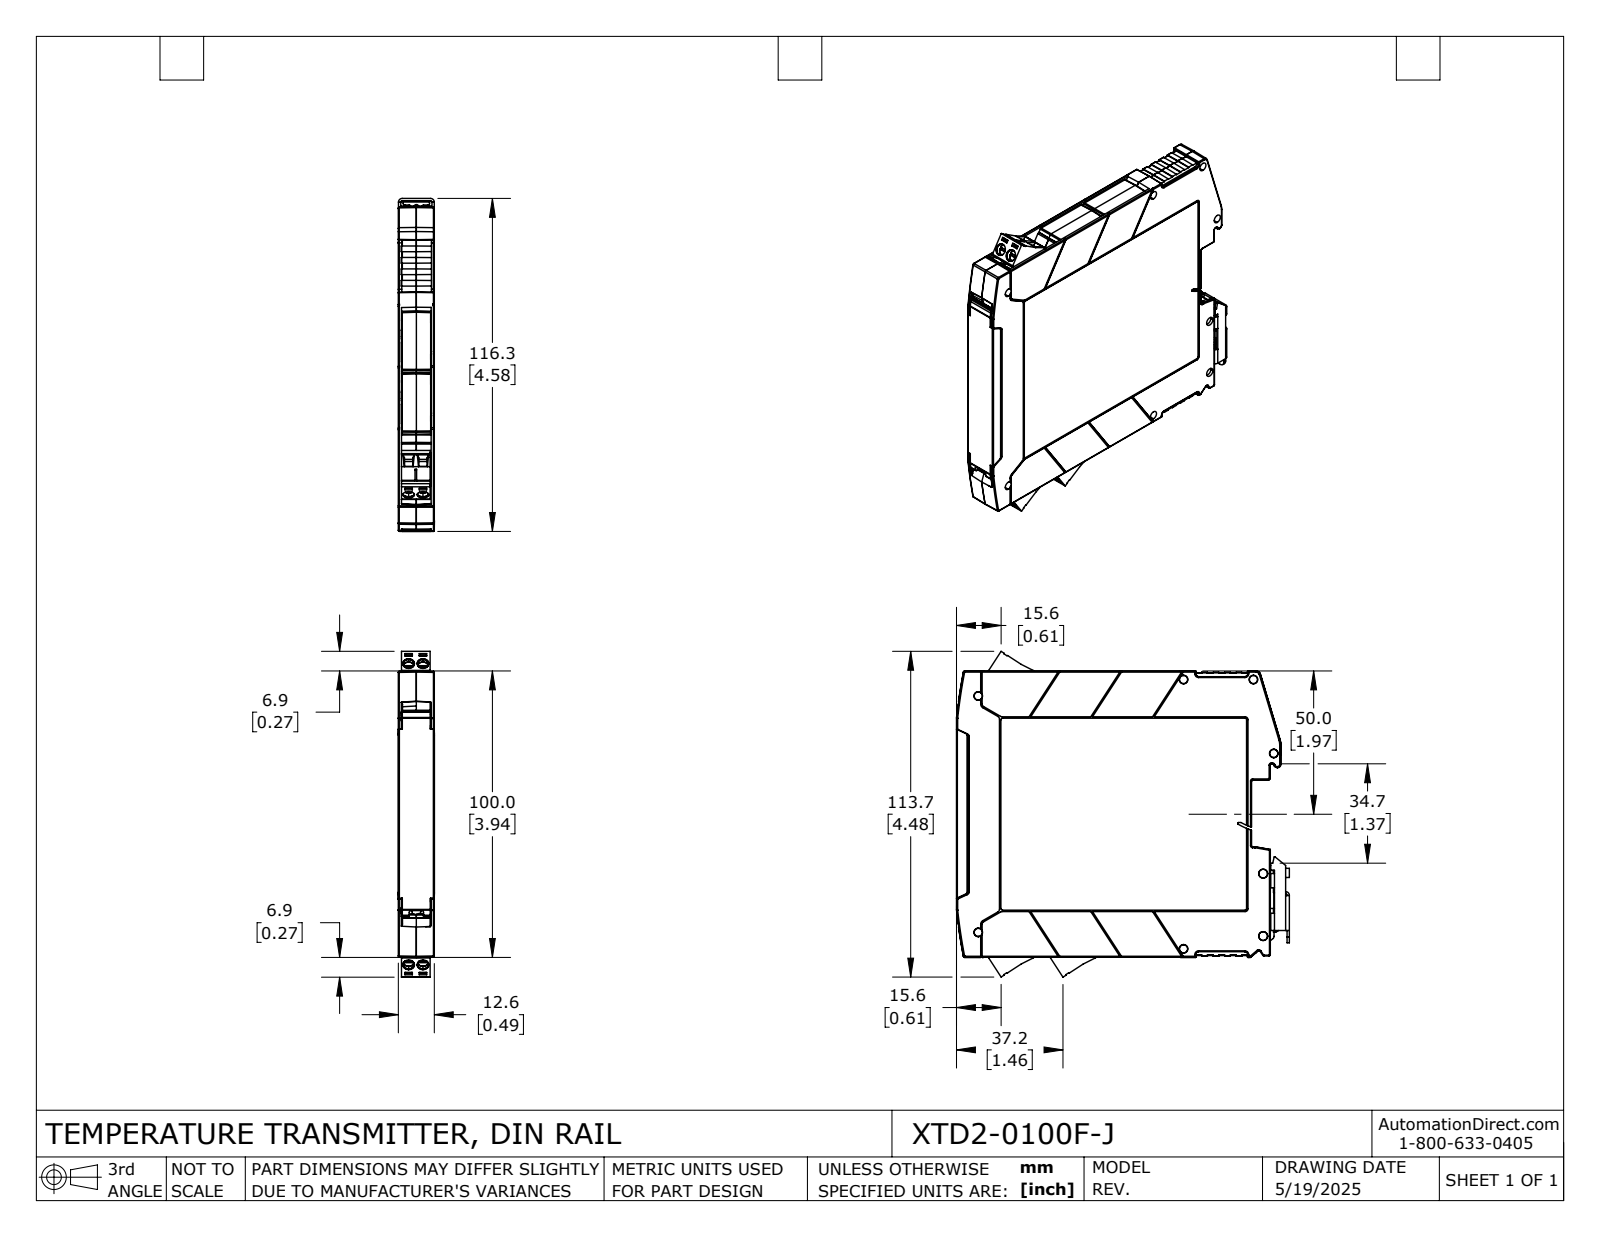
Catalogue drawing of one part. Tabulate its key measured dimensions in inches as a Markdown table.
| quantity | value |
| --- | --- |
| part name | XTD2-0100F-J |
| STEP written by | SolidWorks 2024 (AUTOMOTIVE_DESIGN) |
| units | inches |
| bodies | 14 solids, 3337 faces (1910 planar, 596 cylindrical, 831 other) |
| overall size | 4.577 × 4.478 × 0.496 |
| volume | 2.41 in³ |
| surface area | 101.5 in² |
| round holes (diameter × count) | 0.063 × 6, 0.11 × 6, 0.152 × 6, 0.159 × 6 |
| round bosses / shafts (diameter × count) | 0.156 × 6, 0.098 × 6, 0.059 × 2, 0.053 × 2 |
| partial cylindrical surfaces (radius × count) | 0.008 × 89, 0.012 × 78, 0.02 × 71, 0.039 × 22, 0.004 × 20, 0.016 × 13, 0.006 × 12, 0.028 × 8 |
| main face-to-face distances | 0.049, 0.445, 0.494, 0.396, 0.043, 0.451, 0.402, 0.031, 0.198, 0.247 |
| hole center spacings | 0.197, 0.464, 0.504, 0.713, 0.739 |
